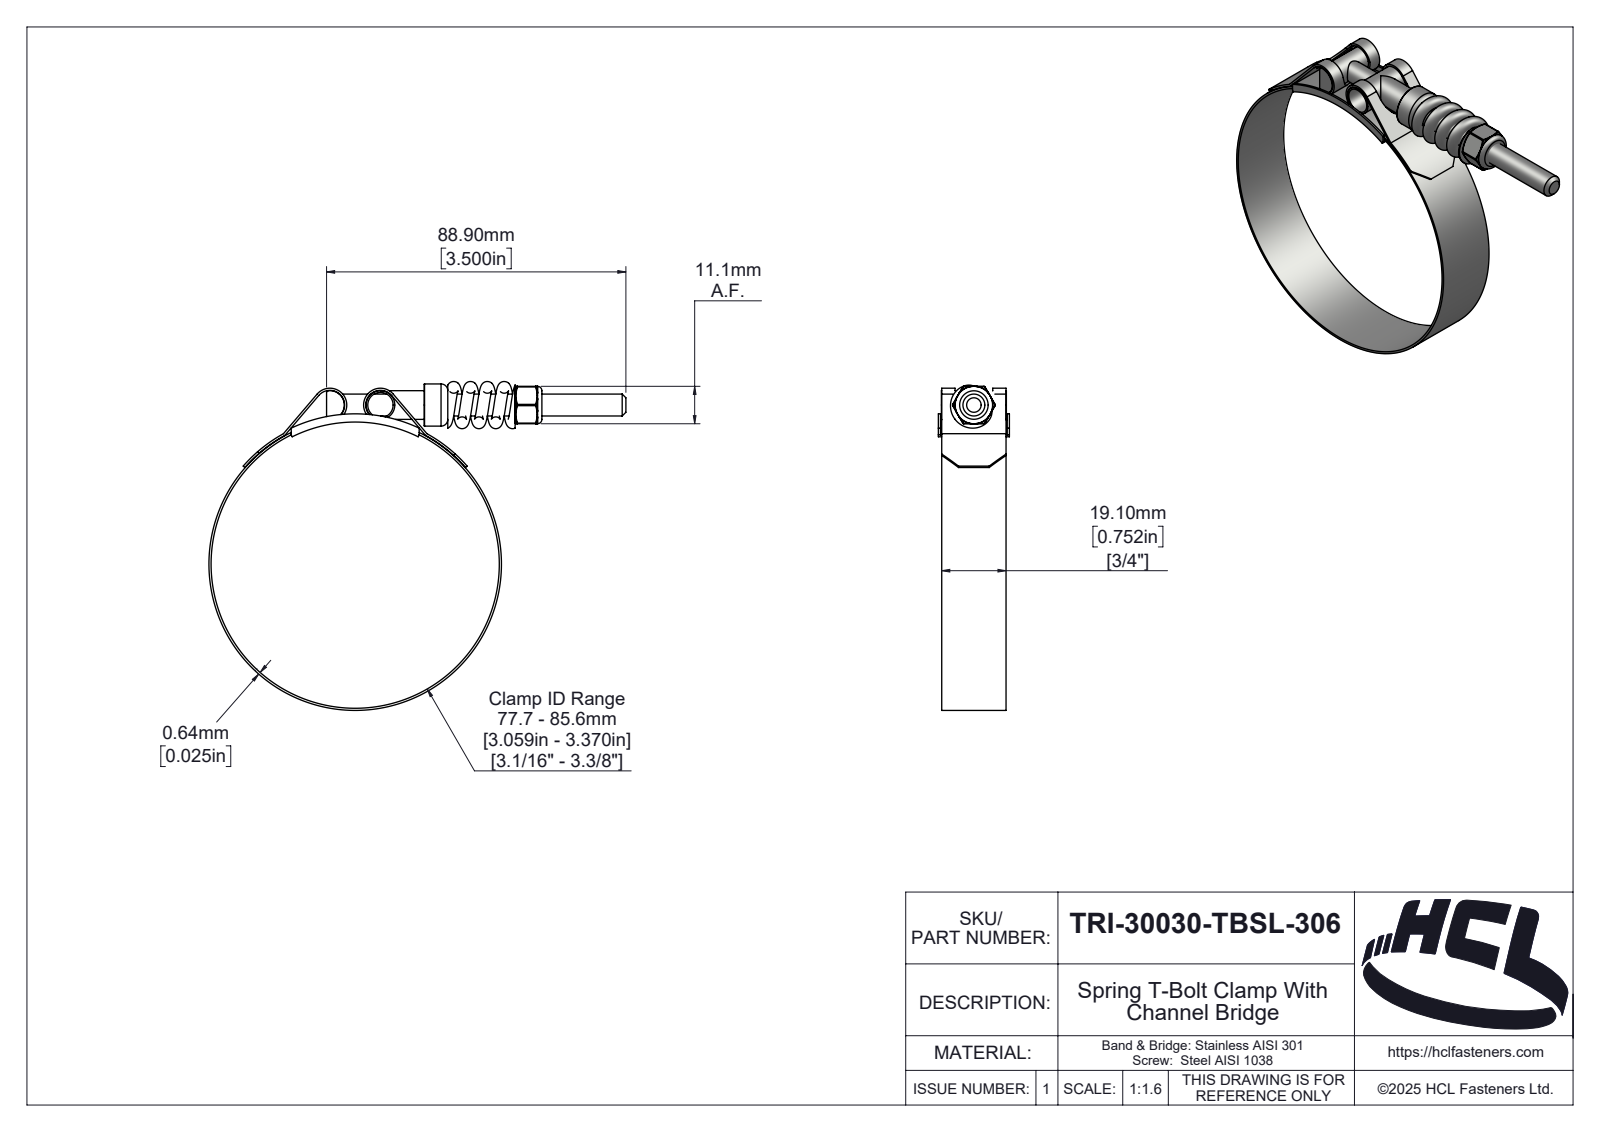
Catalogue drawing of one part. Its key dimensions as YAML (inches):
part_name: "TRI-30030-TBSL-306"
step_written_by: "SolidWorks 2025 (AUTOMOTIVE_DESIGN)"
units: inches
bodies: {solids: 7, faces: 332, planar: 48, cylindrical: 122, other: 162}
overall_size: [4.915, 3.845, 0.831]
volume: 0.674
surface_area: 33.46
round_holes:
  - {diameter: 0.213, count: 1}
  - {diameter: 0.25, count: 1}
  - {diameter: 0.256, count: 1}
  - {diameter: 0.296, count: 1}
  - {diameter: 3.37, count: 1}
round_bosses_or_shafts:
  - {diameter: 0.335, count: 2}
  - {diameter: 3.42, count: 1}
  - {diameter: 0.493, count: 1}
partial_cylinders:
  - {radius: 0.015, count: 6}
  - {radius: 0.02, count: 2}
  - {radius: 0.172, count: 2}
  - {radius: 0.197, count: 2}
  - {radius: 0.023, count: 1}
  - {radius: 0.095, count: 1}
  - {radius: 0.119, count: 1}
  - {radius: 0.126, count: 1}
face_to_face_distances: [0.025, 0.752, 0.039, 0.791, 0.806, 0.014, 0.766, 2.205, 0.437, 0.035]
hole_center_spacings: [1.882]
